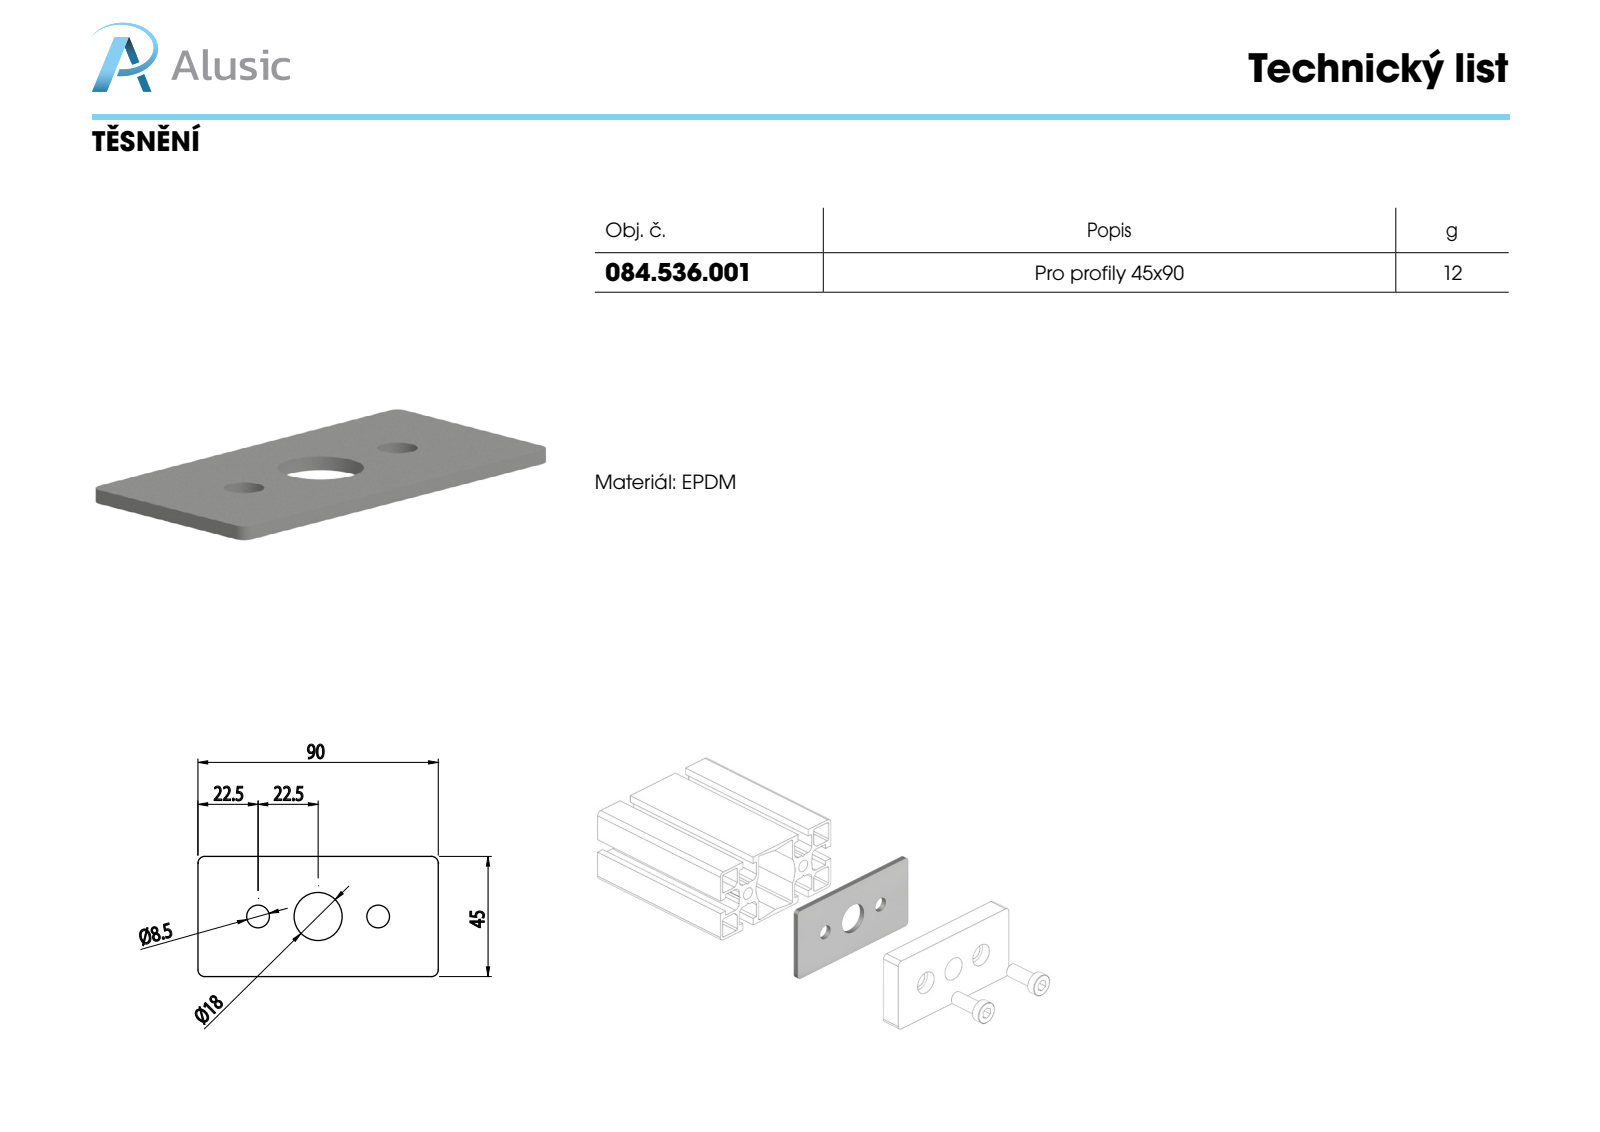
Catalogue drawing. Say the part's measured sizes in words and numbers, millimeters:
The part is named "084.536.001". Its 3-D file was written by "SolidWorks 2011 (CONFIG_CONTROL_DESIGN)". It is 1 solid with 16 faces: 6 planar, 10 cylindrical and 0 other. Overall it measures 90 by 45 by 3 millimeters. Its volume is 11 030 cubic millimeters and its surface area 8 480 square millimeters. Round holes: 2 of diameter 8.5, 1 of diameter 18. Partial cylindrical surfaces (rounded edges, fillets, slot ends): 4 of radius 2.5. The main face-to-face distances are 3, 45, 90. The hole center spacings are 22.5, 45.
